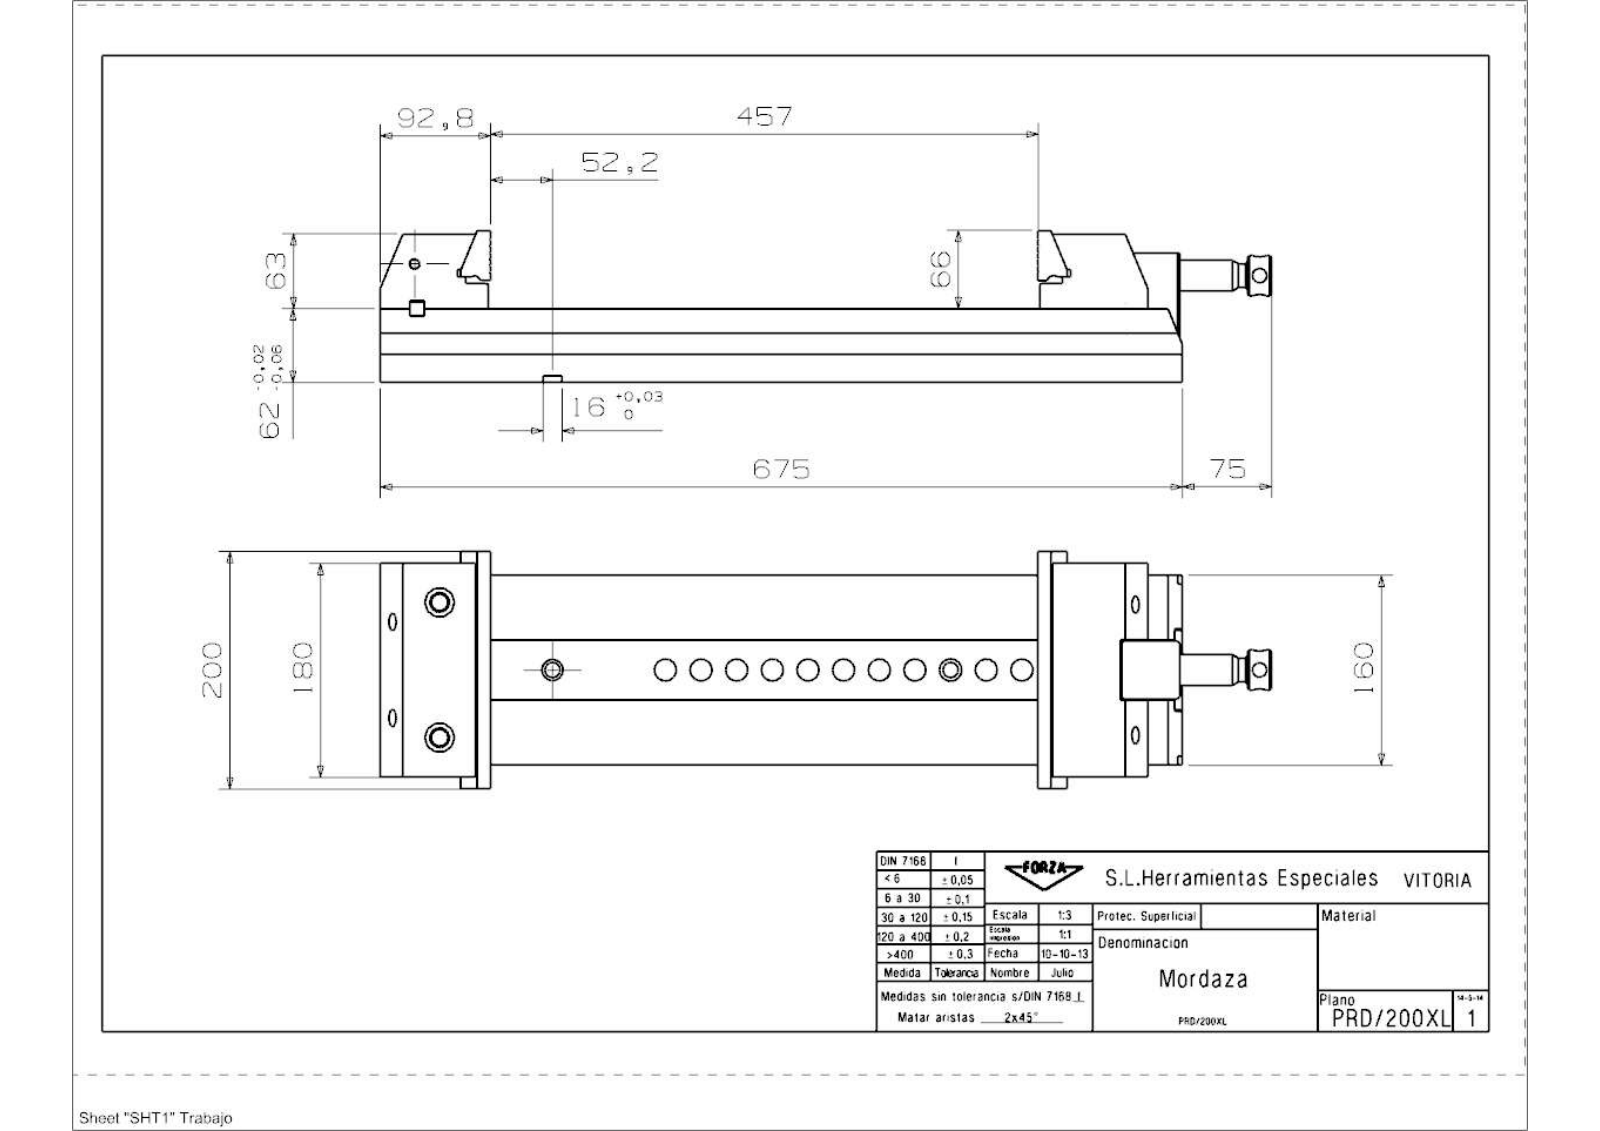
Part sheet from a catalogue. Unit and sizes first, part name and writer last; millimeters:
Units: millimetres
Overall size (bounding box): 750 × 200 × 127.95
Round holes (diameter × count): ⌀15 ×6, ⌀5.19 ×5, ⌀13 ×5, ⌀6.99 ×4, ⌀8.5 ×4, ⌀10 ×4, ⌀19 ×4, ⌀8.78 ×3, ⌀10.58 ×3, ⌀12 ×2, ⌀12.38 ×2, ⌀14.38 ×2
Round bosses / shafts (diameter × count): ⌀34 ×1, ⌀33.8 ×1, ⌀26 ×1, ⌀20 ×1, ⌀16.5 ×1
Partial cylindrical surfaces — rounded edges, fillets, slot ends (radius × count): R0.4 ×24, R1.5 ×4, R8 ×4, R20 ×4, R1.6 ×2, R6 ×2, R7 ×2, R4 ×1
Main face-to-face distances: 62, 29.6, 32.4, 125, 2, 160, 27.6, 60, 7.5, 152.5
Hole centre spacings: 14.5, 95.5, 81, 110, 68, 16.47, 16.55, 30
Volume: 7 113 000 mm³ · Surface area: 713 027 mm²
Bodies: 11 solids, 452 faces (269 planar, 130 cylindrical, 53 other)
Part name (STEP PRODUCT): 30150070 Montaje Taco Hus; PRD_200XL_Mordaza
STEP written by: SIEMENS PLM Software NX 9.0 (CONFIG_CONTROL_DESIGN)
